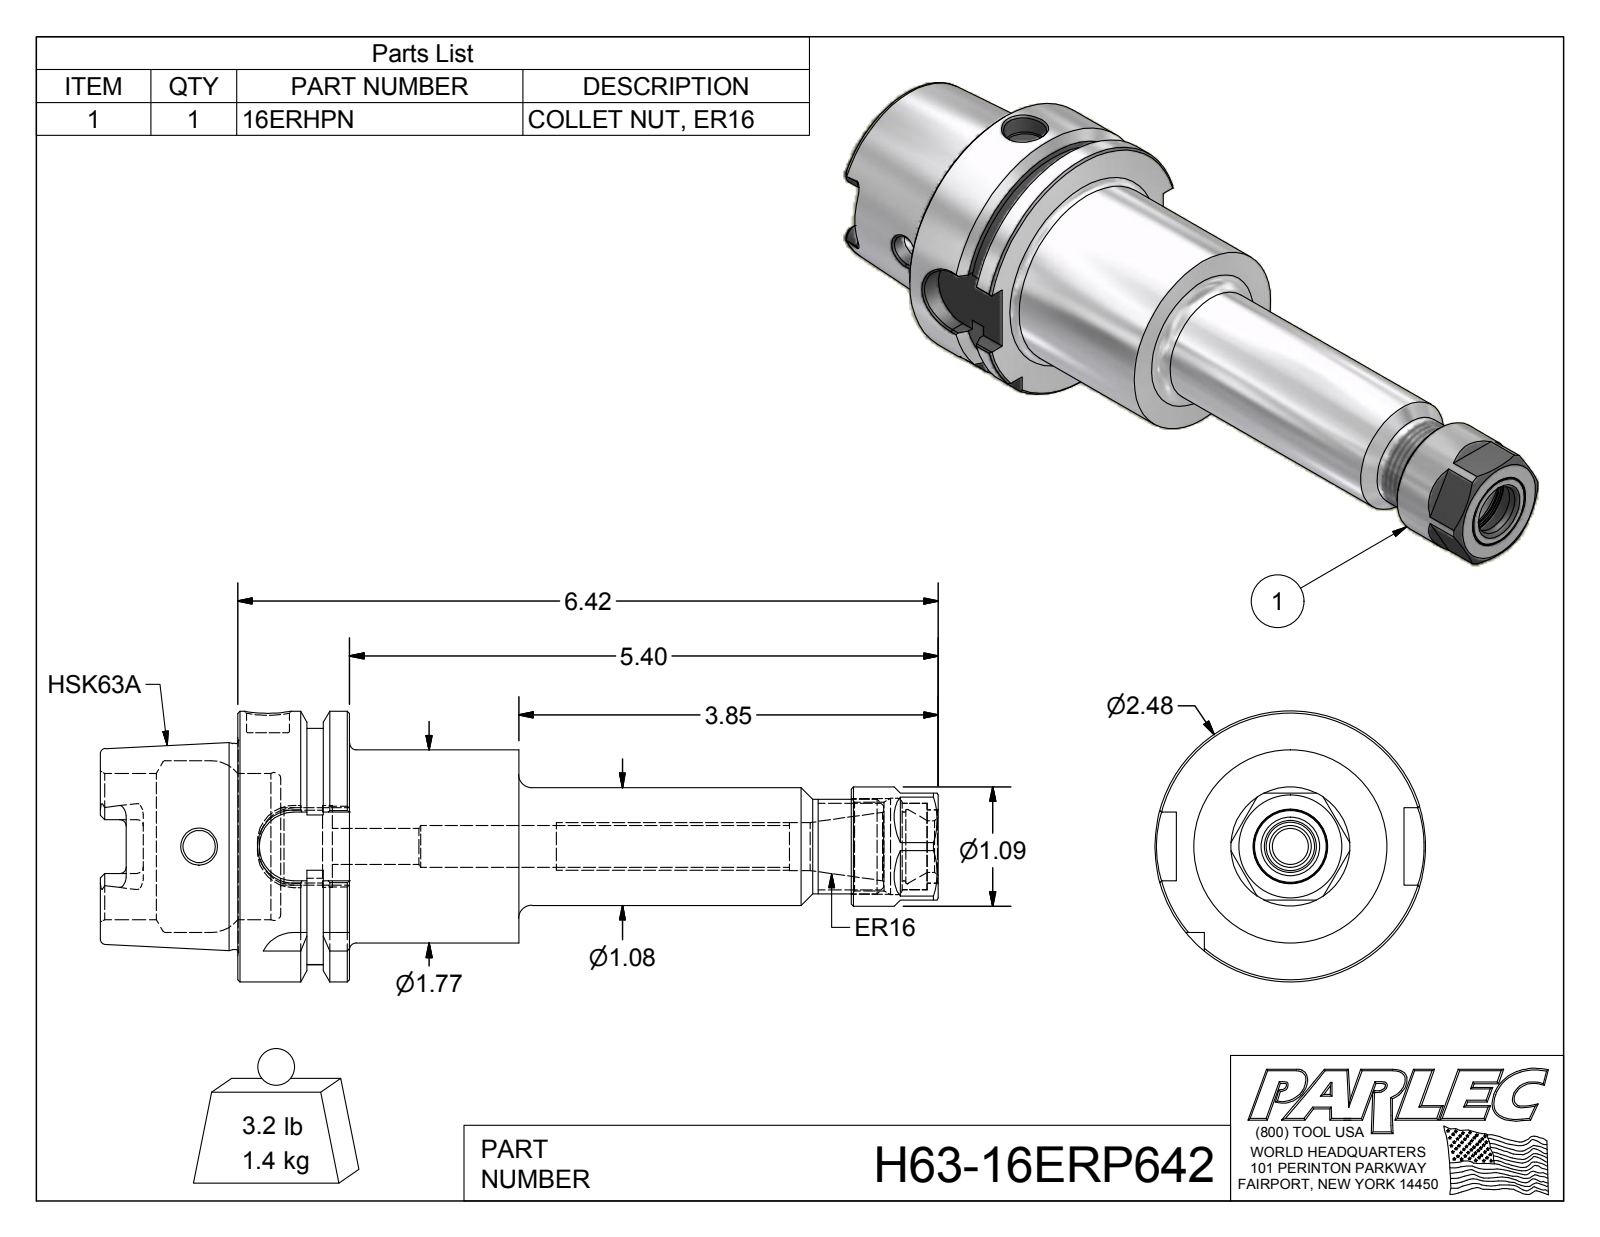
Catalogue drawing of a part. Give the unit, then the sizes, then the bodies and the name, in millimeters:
Units: millimetres
Overall size (bounding box): 195.1 × 63 × 63
Round holes (diameter × count): ⌀7.5 ×1, ⌀8.4 ×1, ⌀9.7 ×1, ⌀10 ×1, ⌀11.2 ×1, ⌀12 ×1, ⌀16 ×1, ⌀16.9 ×1, ⌀17.1 ×1, ⌀17.3 ×1, ⌀19 ×1, ⌀20.2 ×1
Round bosses / shafts (diameter × count): ⌀63 ×1, ⌀48 ×1, ⌀45 ×1, ⌀27.7 ×1, ⌀27.4 ×1, ⌀22 ×1, ⌀20.1 ×1, ⌀17 ×1
Partial cylindrical surfaces — rounded edges, fillets, slot ends (radius × count): R1.5 ×6, R2.9 ×4, R8 ×4, R27.5 ×1
Main face-to-face distances: 26, 65.4, 39.4, 10, 16, 55.4, 32, 42, 58, 97.4
Volume: 185 800 mm³ · Surface area: 43 460 mm²
Bodies: 3 solids, 184 faces (73 planar, 47 cylindrical, 64 other)
Part name (STEP PRODUCT): H63-16ERP642; H63-16ER6-1; 16ERHPN
STEP written by: Autodesk Inventor 2012 (AUTOMOTIVE_DESIGN)
